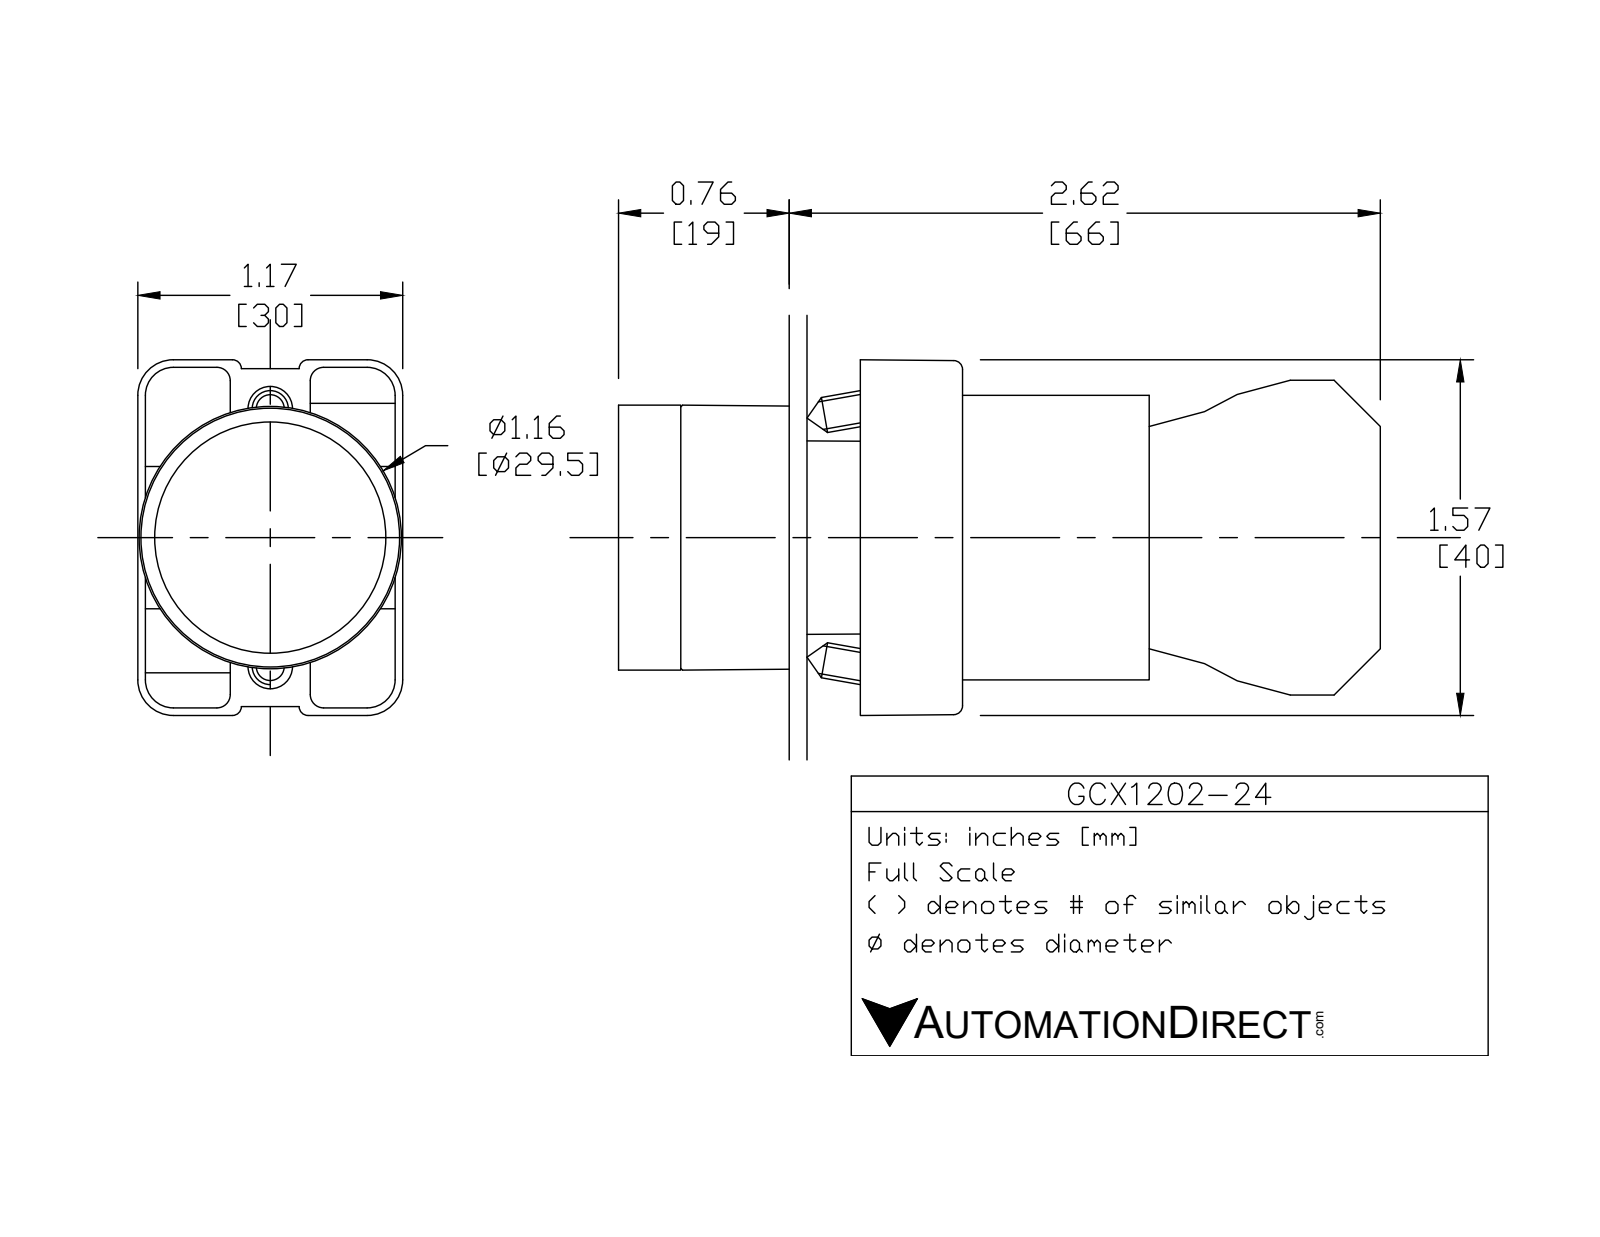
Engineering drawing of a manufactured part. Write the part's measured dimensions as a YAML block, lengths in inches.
part_name: "ECX1050; GCX1202-24; GCX1202 OPERATOR; ecx1040 (+1 more)"
step_written_by: "SolidWorks 2016 (AUTOMOTIVE_DESIGN)"
units: inches
bodies: {solids: 8, faces: 431, planar: 252, cylindrical: 148, other: 31}
overall_size: [3.319, 1.581, 1.177]
volume: 2.794
surface_area: 38.75
round_holes:
  - {diameter: 0.079, count: 2}
  - {diameter: 0.124, count: 2}
  - {diameter: 0.13, count: 2}
  - {diameter: 0.087, count: 1}
  - {diameter: 0.197, count: 1}
  - {diameter: 0.469, count: 1}
  - {diameter: 0.878, count: 1}
  - {diameter: 0.888, count: 1}
  - {diameter: 1.024, count: 1}
round_bosses_or_shafts:
  - {diameter: 0.157, count: 4}
  - {diameter: 1.175, count: 1}
  - {diameter: 1.004, count: 1}
  - {diameter: 0.945, count: 1}
  - {diameter: 0.856, count: 1}
  - {diameter: 0.78, count: 1}
  - {diameter: 0.504, count: 1}
partial_cylinders:
  - {radius: 0.059, count: 24}
  - {radius: 0.041, count: 12}
  - {radius: 0.124, count: 12}
  - {radius: 0.157, count: 12}
  - {radius: 0.039, count: 8}
  - {radius: 0.128, count: 2}
  - {radius: 0.02, count: 1}
  - {radius: 0.063, count: 1}
face_to_face_distances: [0.827, 2.02, 1.193, 0.579, 1.171, 0.031, 0.276, 0.033, 0.748, 0.573]
hole_center_spacings: [0.236, 0.544, 0.472, 0.49]
